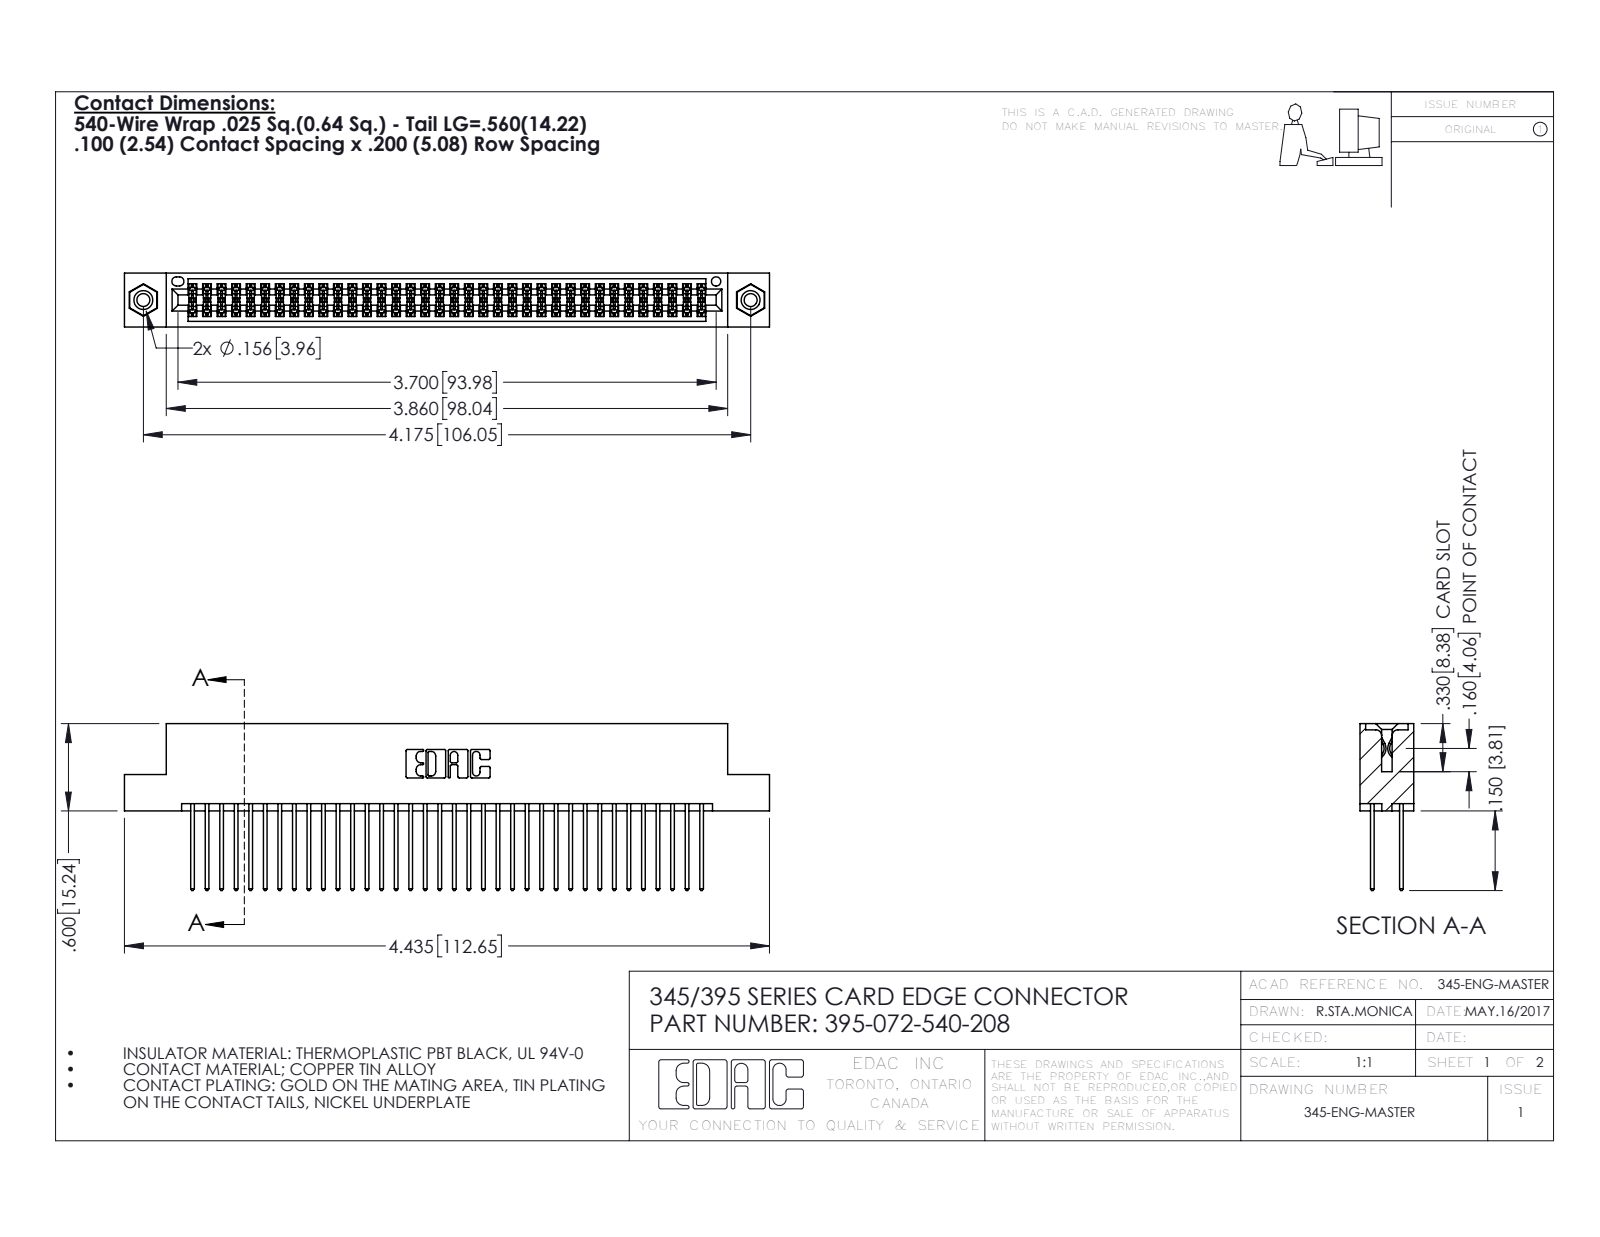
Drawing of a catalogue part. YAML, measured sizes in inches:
part_name: "395-072-540-208; 345-292-001_345-293-140; 345-250-001_345-250-003-102; 345 Part_Flush Mounting Lugs - 0.156 Dia-TI"
step_written_by: "SolidWorks 2016 (CONFIG_CONTROL_DESIGN)"
units: inches
bodies: {solids: 75, faces: 3786, planar: 2488, cylindrical: 1282, other: 16}
overall_size: [4.435, 1.147, 0.37]
volume: 0.681
surface_area: 27.36
round_holes:
  - {diameter: 0.089, count: 2}
  - {diameter: 0.125, count: 2}
  - {diameter: 0.156, count: 2}
  - {diameter: 0.064, count: 1}
round_bosses_or_shafts:
  - {diameter: 0.155, count: 2}
partial_cylinders:
  - {radius: 0.006, count: 108}
  - {radius: 0.01, count: 72}
  - {radius: 0.01, count: 22}
  - {radius: 0.007, count: 6}
  - {radius: 0.031, count: 6}
  - {radius: 0.026, count: 3}
  - {radius: 0.014, count: 2}
  - {radius: 0.019, count: 2}
face_to_face_distances: [0.072, 0.298, 0.2, 0.098, 0.272, 0.025, 0.37, 0.225, 0.175, 0.149]
hole_center_spacings: [0.27, 3.939, 4.175]
